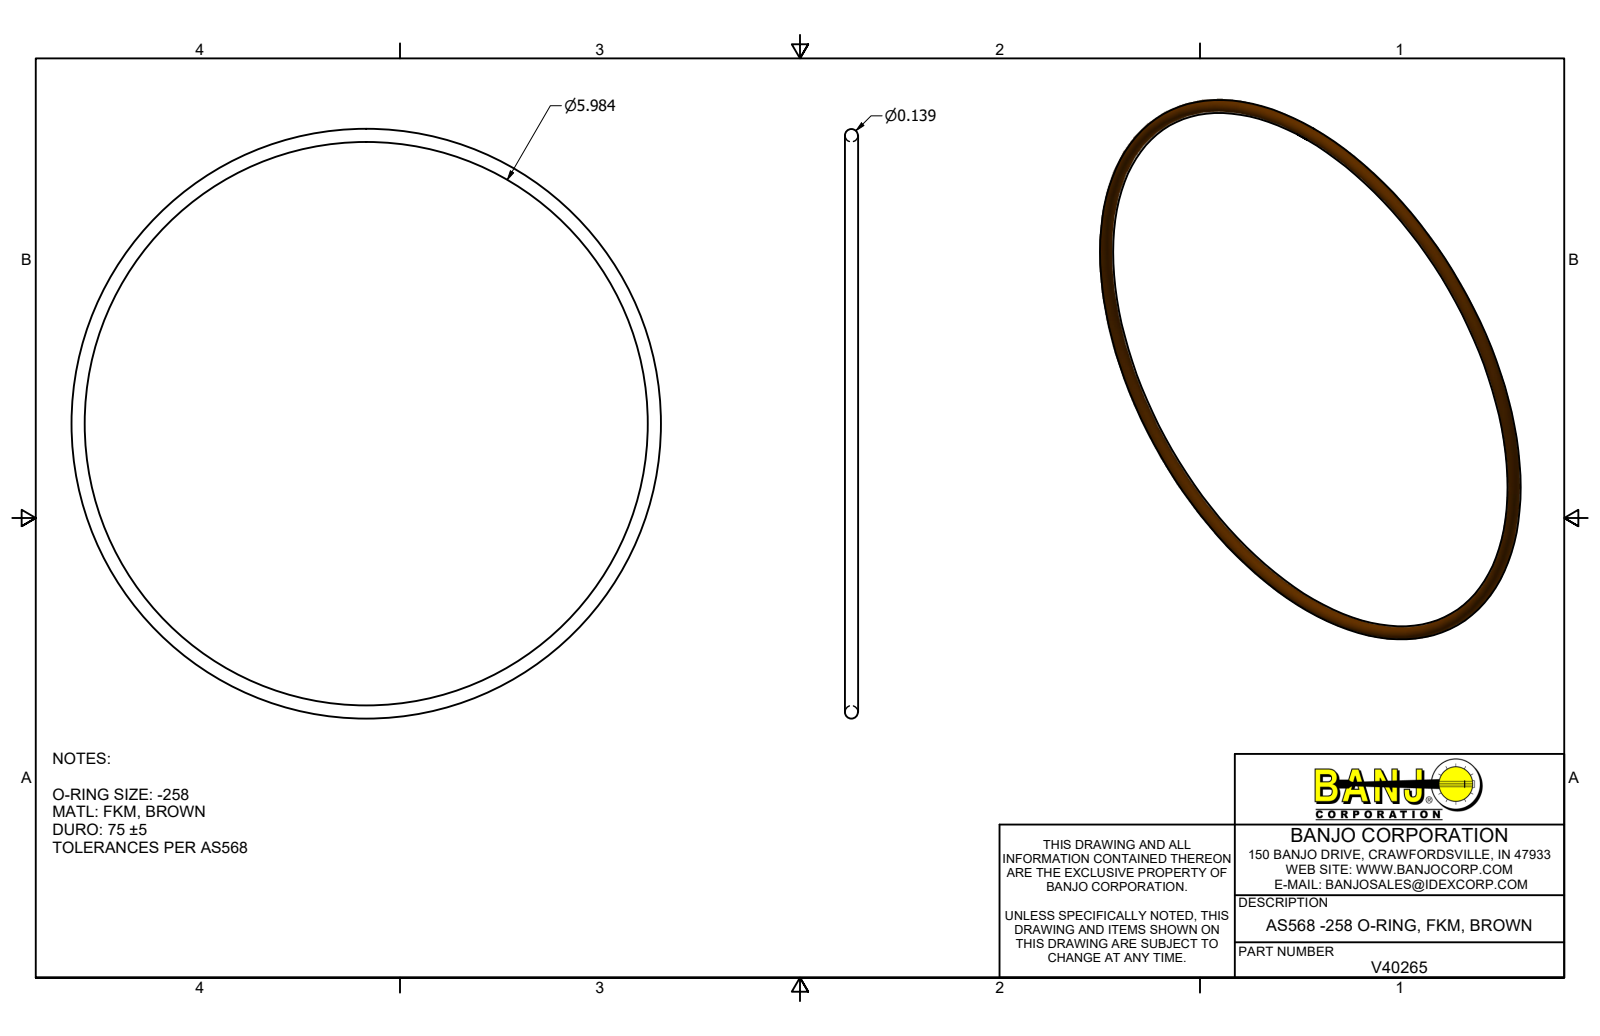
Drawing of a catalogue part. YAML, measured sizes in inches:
part_name: "V40265"
step_written_by: "Autodesk Inventor 2022 (AUTOMOTIVE_DESIGN)"
units: inches
bodies: {solids: 1, faces: 1, planar: 0, cylindrical: 0, other: 1}
overall_size: [6.262, 6.262, 0.139]
volume: 0.292
surface_area: 8.4
